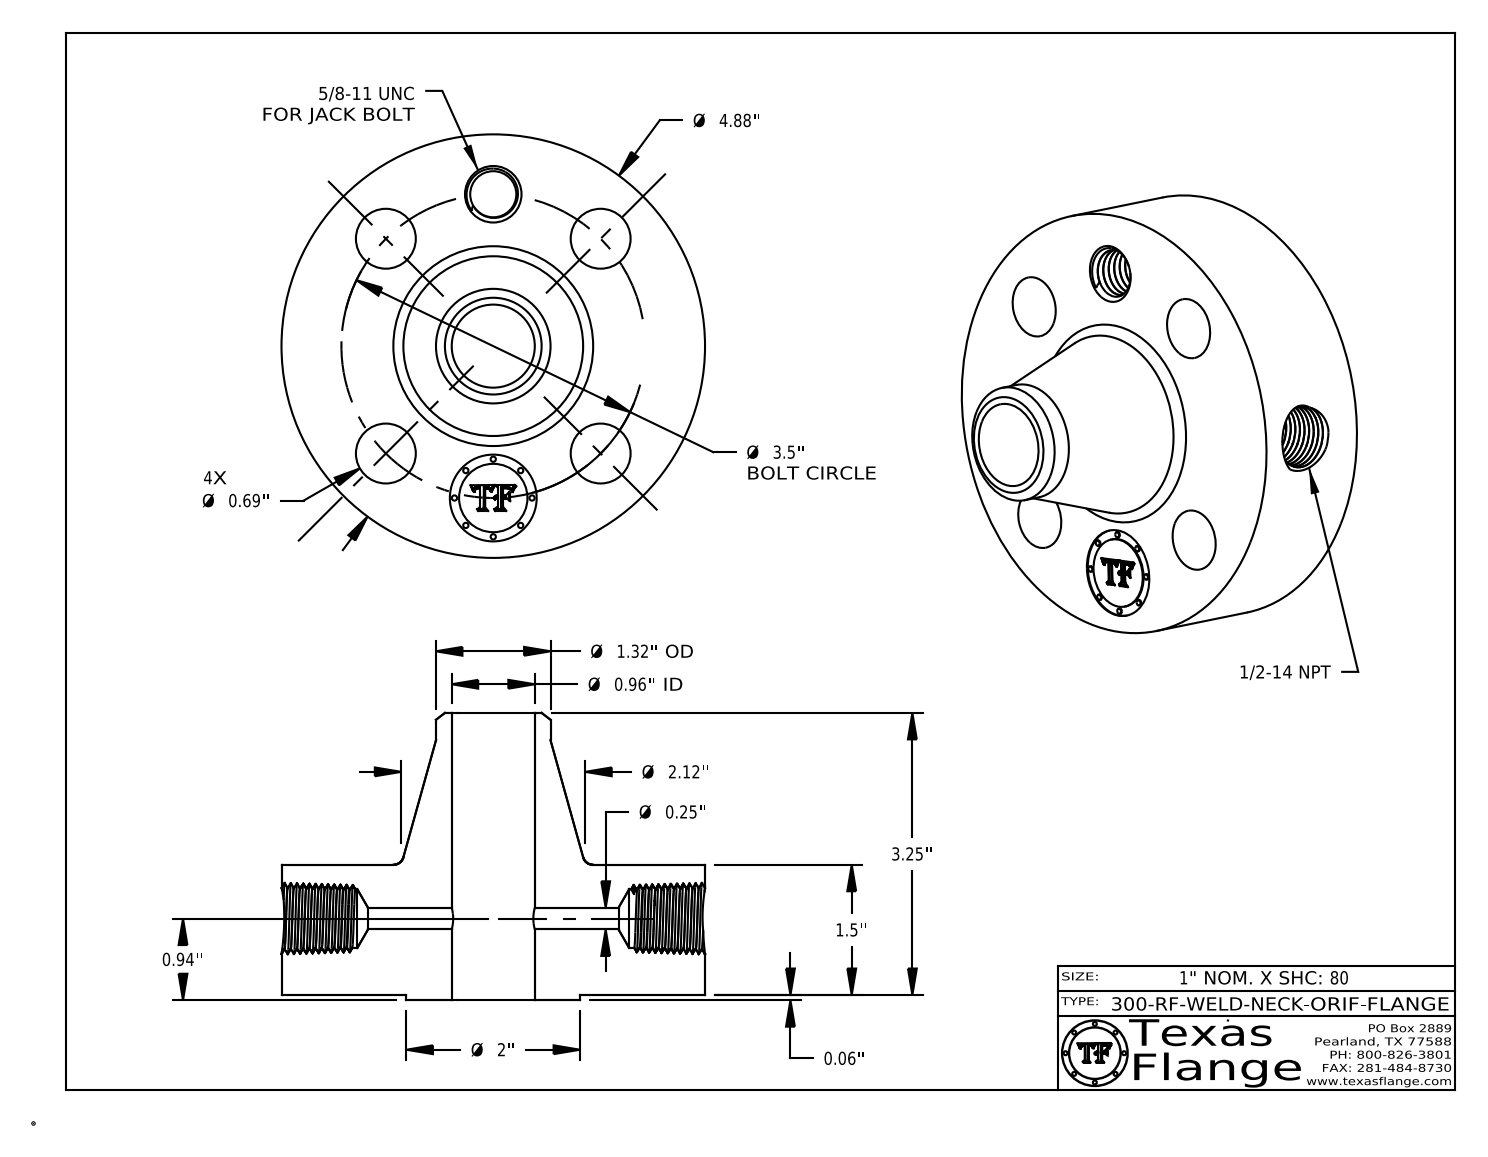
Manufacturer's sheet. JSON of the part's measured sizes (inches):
{"part_name": "300-RF-WELD-NECK", "step_written_by": "CATIA V5 STEP AP214 (AUTOMOTIVE_DESIGN)", "units": "inches", "bodies": {"solids": 1, "faces": 764, "planar": 369, "cylindrical": 87, "other": 308}, "overall_size": [4.88, 4.88, 3.31], "volume_in3": 26.17, "surface_area_in2": 97.95, "round_holes": [[0.69, 4], [0.25, 1], [0.531, 1], [0.672, 1], [0.957, 1], [1, 1]], "round_bosses_or_shafts": [[0.061, 8], [4.88, 1], [2, 1], [1.32, 1], [0.788, 1]], "face_to_face_distances": [1.5, 0.06, 1.56, 1.545, 1.485, 0.015, 3.31, 3.25, 1.765, 1.75], "hole_center_spacings": [1.75, 1.339, 2.475, 3.233, 3.5]}
